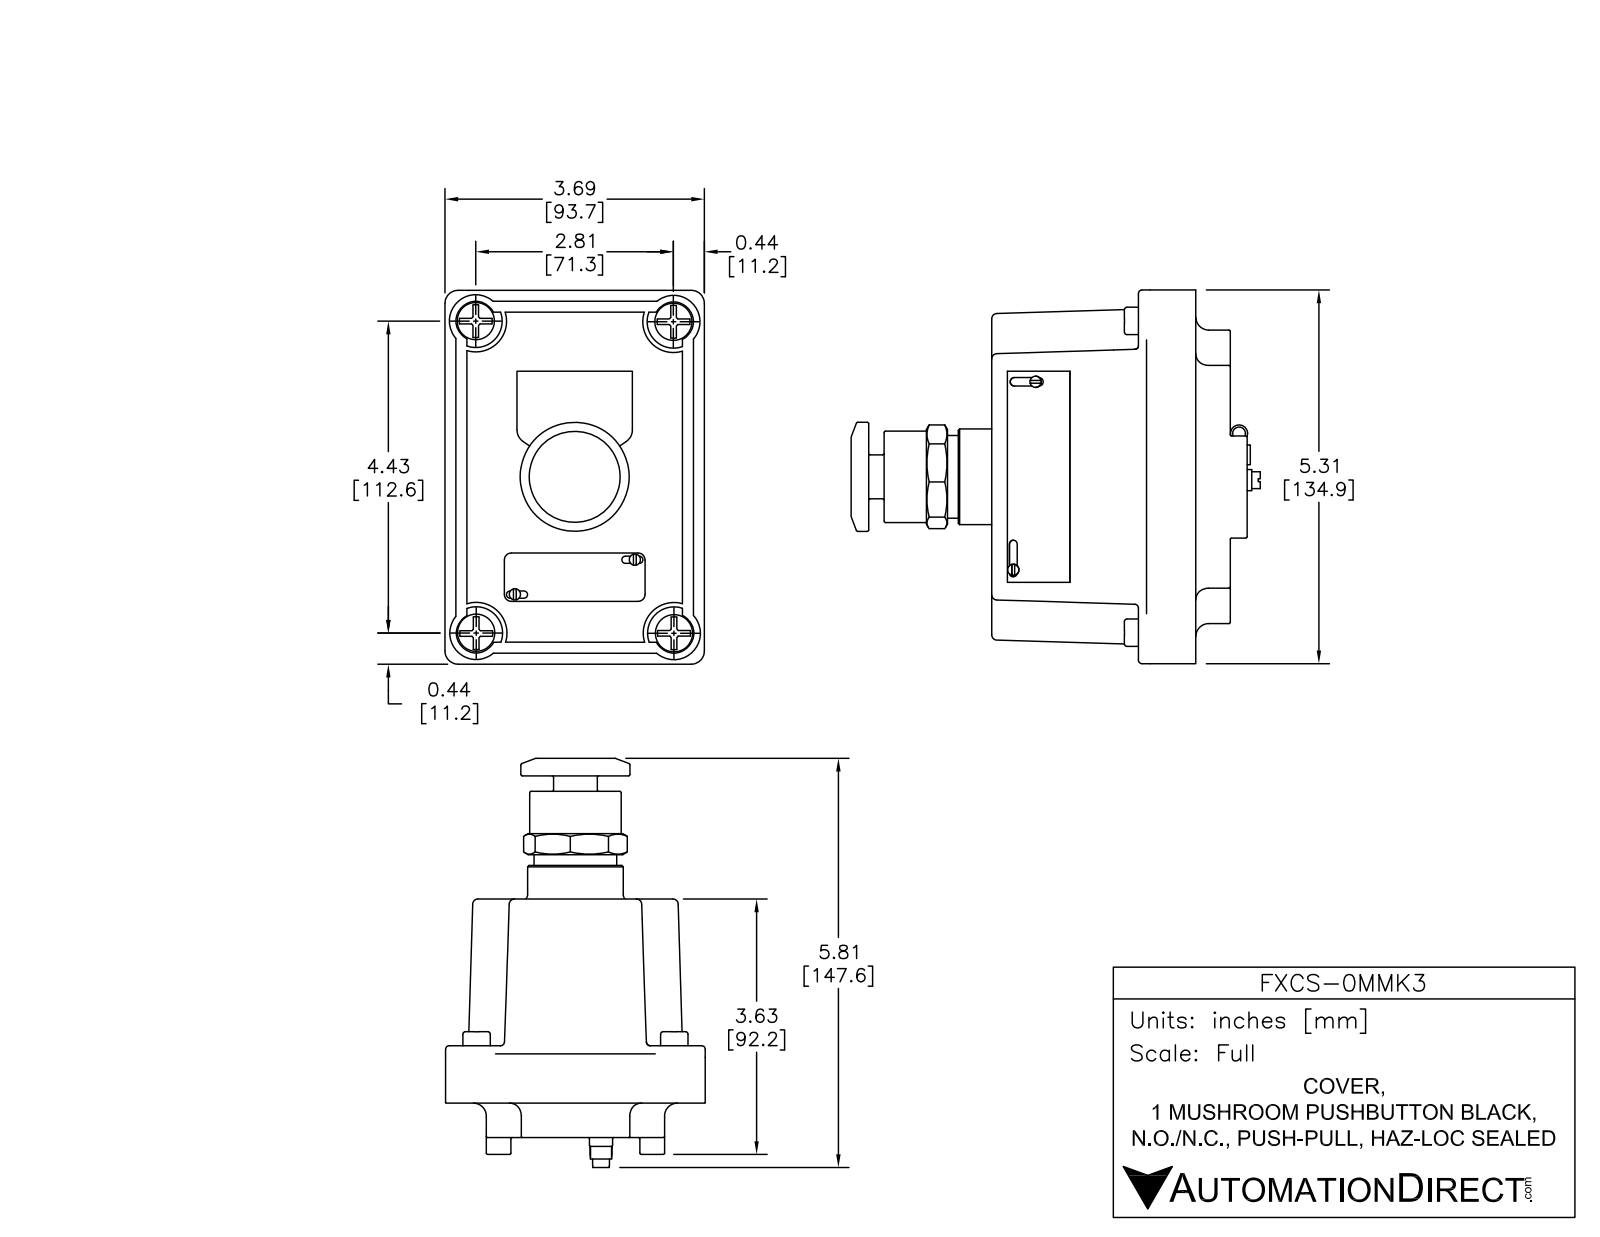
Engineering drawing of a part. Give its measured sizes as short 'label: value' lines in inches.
name: FXCS-0MMK3
written by: SolidWorks 2015 (AUTOMOTIVE_DESIGN)
unit: in
bodies: 1 solid, 732 faces (302 planar, 155 cylindrical, 275 other)
size: 5.888 × 5.31 × 3.69
volume: 50.6 in³; area: 104.6 in²
holes: 8× ⌀0.16, 1× ⌀0.198
bosses: 6× ⌀0.16, 4× ⌀0.39, 1× ⌀1.55, 1× ⌀1.36, 1× ⌀1.3, 1× ⌀1.175, 1× ⌀0.623, 1× ⌀0.33
rounds: 22× R0.02, 12× R0.05, 4× R0.051, 4× R0.055, 4× R0.06, 4× R0.075, 4× R0.1, 4× R0.185
face distances: 0.49, 3.39, 2.9, 0.02, 3.69, 0.578, 3.111, 1.19, 0.7, 2.2
hole spacings: 0.25, 2.197, 0.5, 2.183, 2.239, 0.75, 2.308, 0.728
